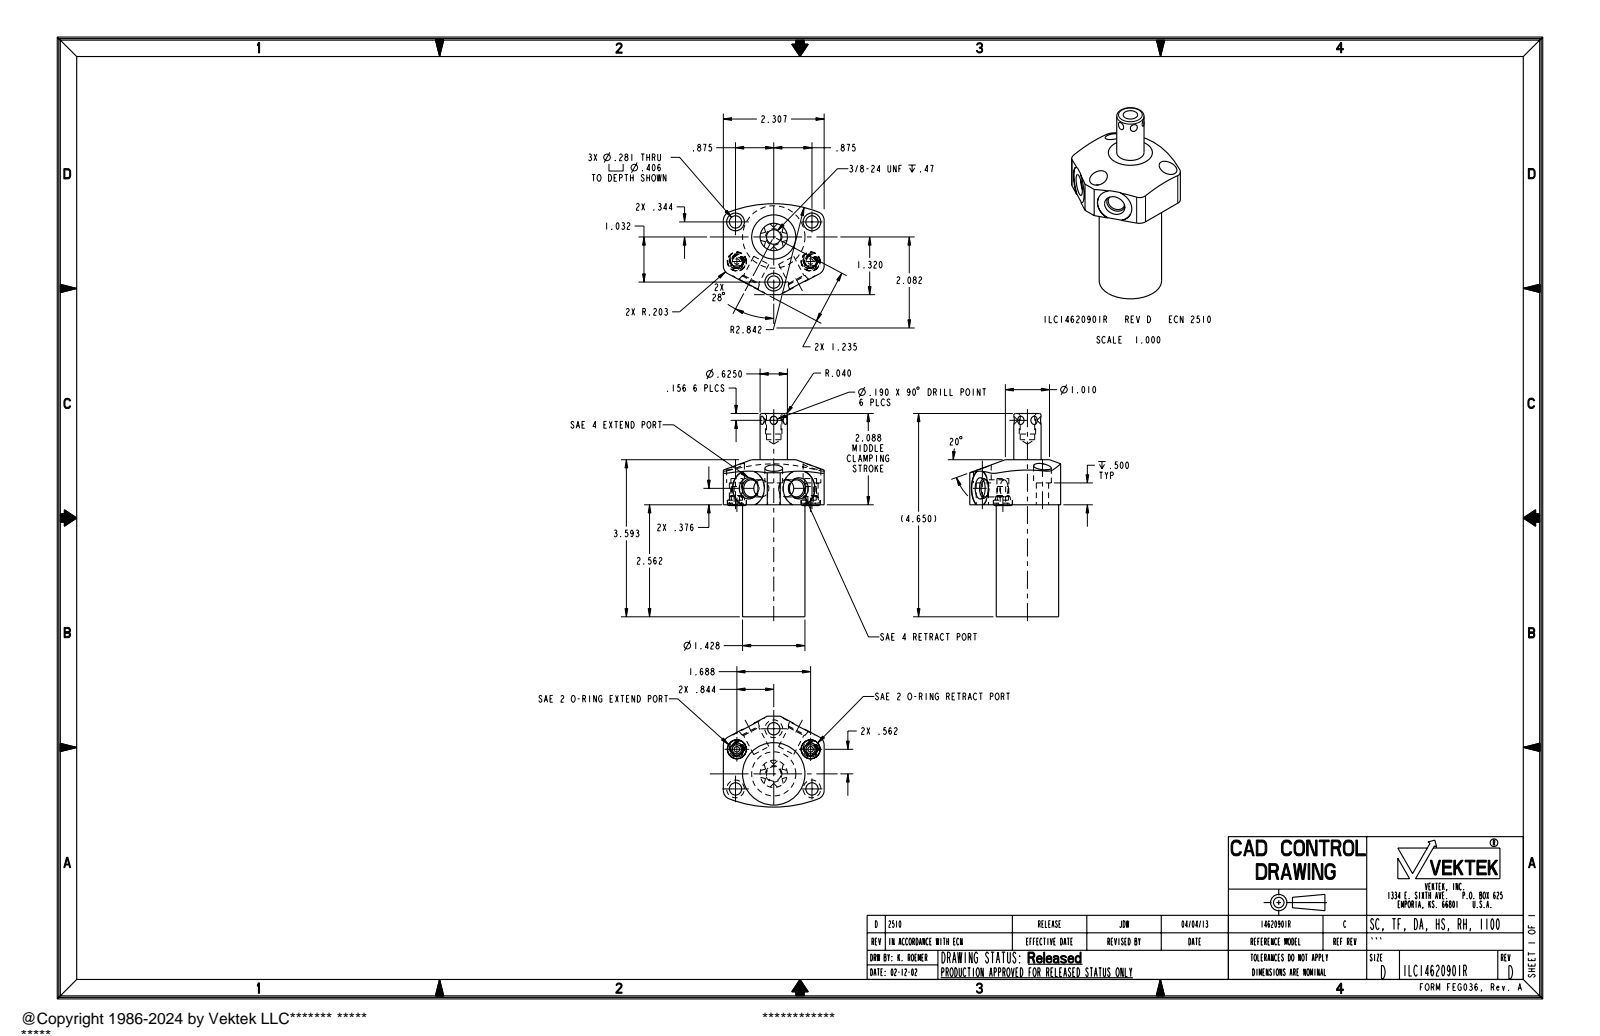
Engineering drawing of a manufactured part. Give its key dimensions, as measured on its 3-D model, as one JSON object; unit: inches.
{"part_name": "ILC14620901R", "step_written_by": "PRO/ENGINEER BY PARAMETRIC TECHNOLOGY CORPORATION, 2007460 (AUTOMOTIVE_DESIGN_CC2)", "units": "inches", "bodies": {"solids": 1, "faces": 132, "planar": 33, "cylindrical": 57, "other": 42}, "overall_size": [4.65, 2.307, 2.08], "volume_in3": 7.645, "surface_area_in2": 35.6, "round_holes": [[0.281, 3], [0.406, 3], [0.125, 2], [0.272, 2], [0.392, 2], [0.438, 2], [0.332, 1]], "round_bosses_or_shafts": [[0.43, 2], [0.256, 2], [0.21, 2], [1.428, 1], [0.625, 1], [0.375, 1]], "partial_cylinders_radius": [[0.203, 4], [0.412, 2], [2.842, 1]], "face_to_face_distances": [2.562, 2.307, 3.593, 1.031, 0.62, 3.062, 0.5, 0.531, 0.1, 0.495], "hole_center_spacings": [0.906, 0.94, 0.966, 1.014, 1.631, 1.943, 1.032, 1.688]}
